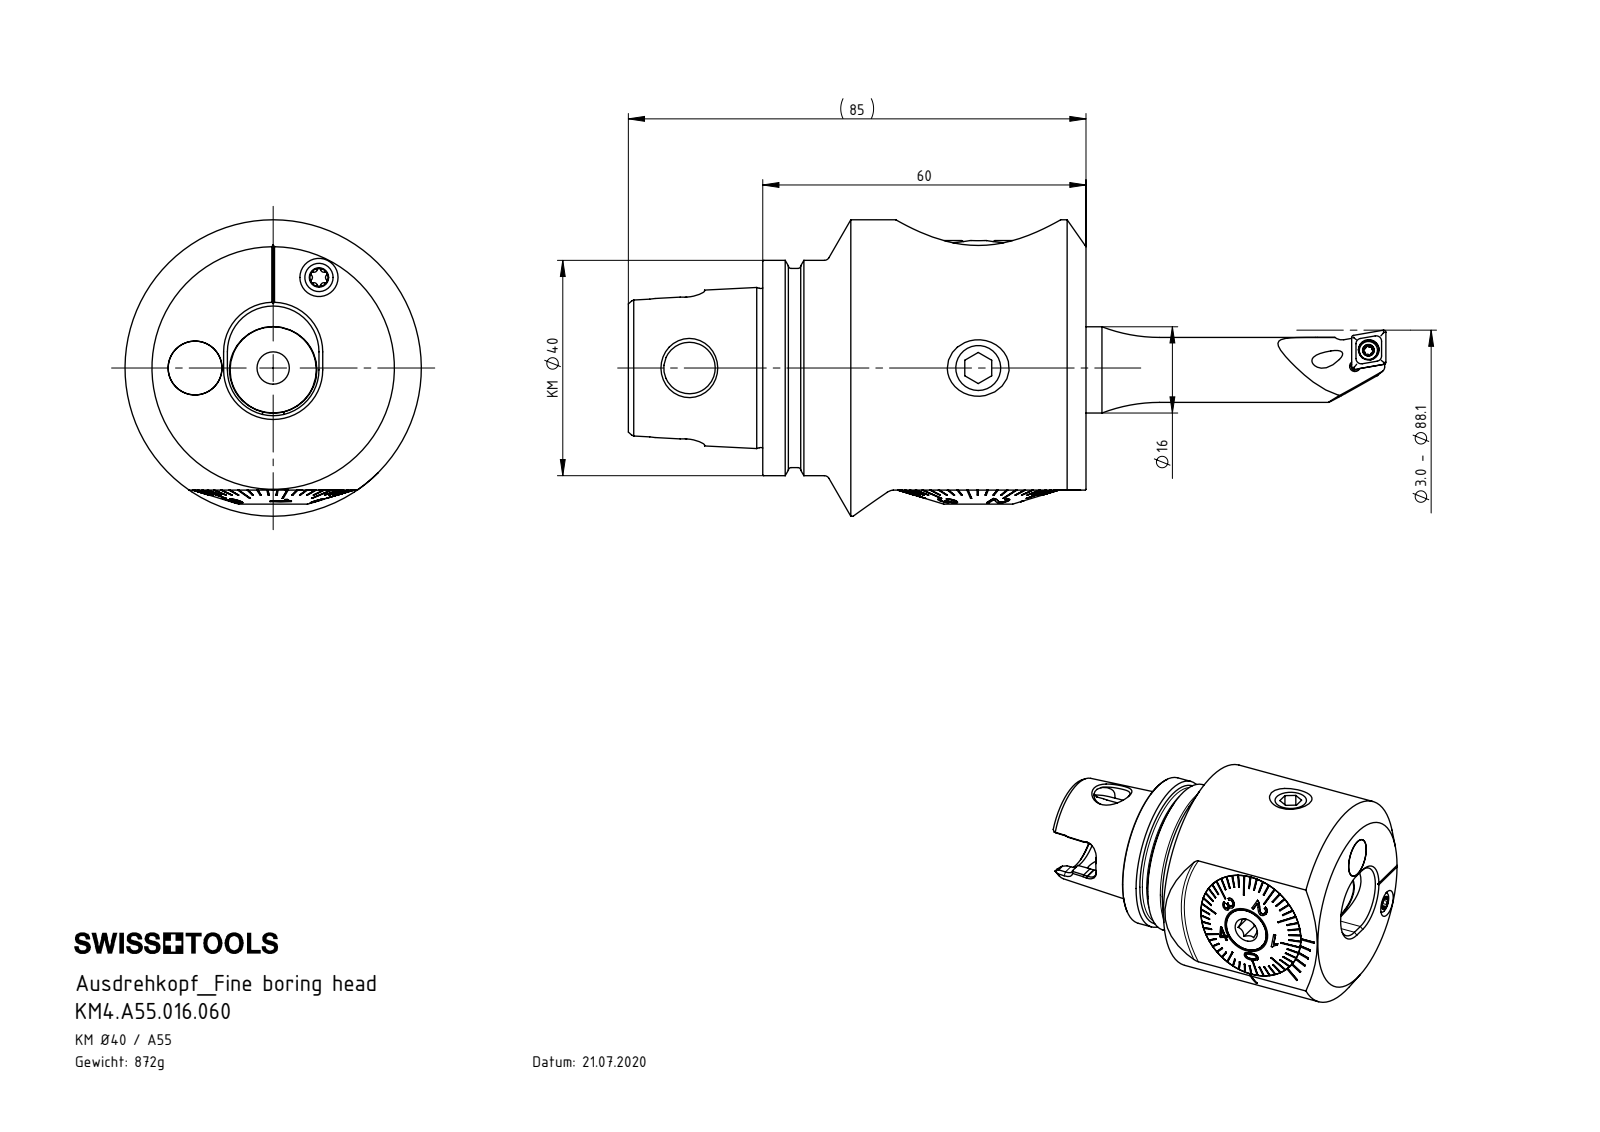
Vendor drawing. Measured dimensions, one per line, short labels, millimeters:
name: Klebstoff D10; A55-BG2.013.005_C; WCB-ER2.001.009_A; KM4.A55.AA4.060 (+8 more)
written by: SolidWorks 2017 (AUTOMOTIVE_DESIGN)
unit: mm
bodies: 14 solids, 650 faces (334 planar, 98 cylindrical, 218 other)
size: 84.95 × 55 × 55
volume: 109 314 mm³; area: 38 173 mm²
holes: 3× ⌀8.5, 1× ⌀1.6, 1× ⌀3.3, 1× ⌀4.2, 1× ⌀6, 1× ⌀8, 1× ⌀9.55, 1× ⌀10, 1× ⌀11.4, 1× ⌀12.4, 1× ⌀14, 1× ⌀14.2
bosses: 3× ⌀10, 1× ⌀55, 1× ⌀39.95, 1× ⌀36.95, 1× ⌀30, 1× ⌀29.98, 1× ⌀29.9, 1× ⌀25
rounds: 6× R0.34, 6× R0.59, 6× R3.1, 4× R1.4, 4× R1.9, 3× R3.2, 2× R2, 2× R4.54
face distances: 5.3, 2.8, 2.5, 6.5, 3.7, 1.2, 60, 16, 5.2, 16.5
hole spacings: 14.5, 7.25, 0.35, 18.83, 19.14, 28.48, 53.6
